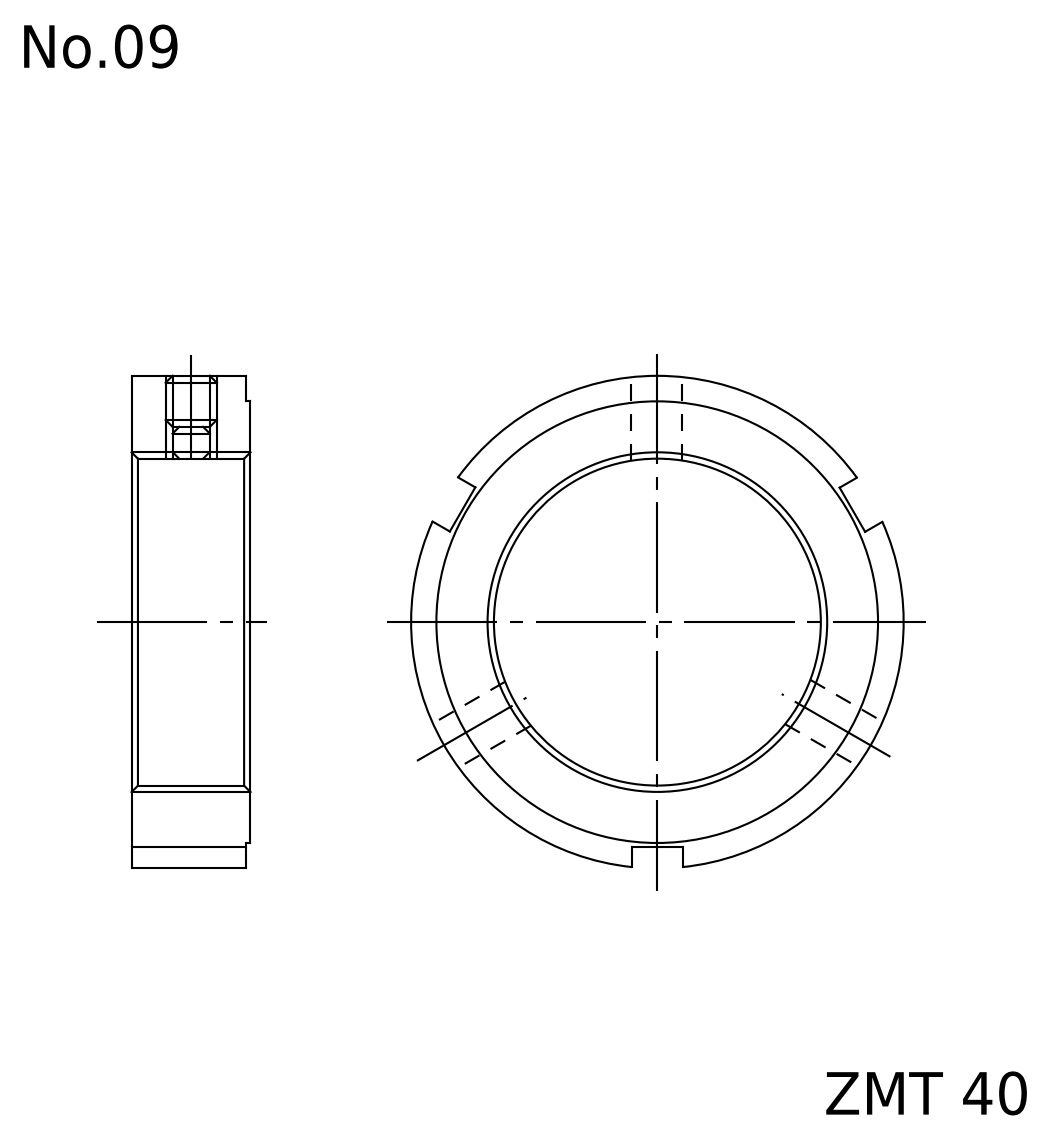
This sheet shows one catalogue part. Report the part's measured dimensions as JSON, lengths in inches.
{"part_name": "FKD ZMT 40", "step_written_by": "Autodesk Inventor 2011 (AUTOMOTIVE_DESIGN)", "units": "inches", "bodies": {"solids": 1, "faces": 20, "planar": 12, "cylindrical": 8, "other": 0}, "overall_size": [2.283, 2.277, 0.551], "volume_in3": 1.1, "surface_area_in2": 11.59, "round_holes": [[0.194, 3], [1.575, 1]], "round_bosses_or_shafts": [[2.283, 1], [2.047, 1]], "face_to_face_distances": [0.551, 0.02, 0.531, 0.236]}
